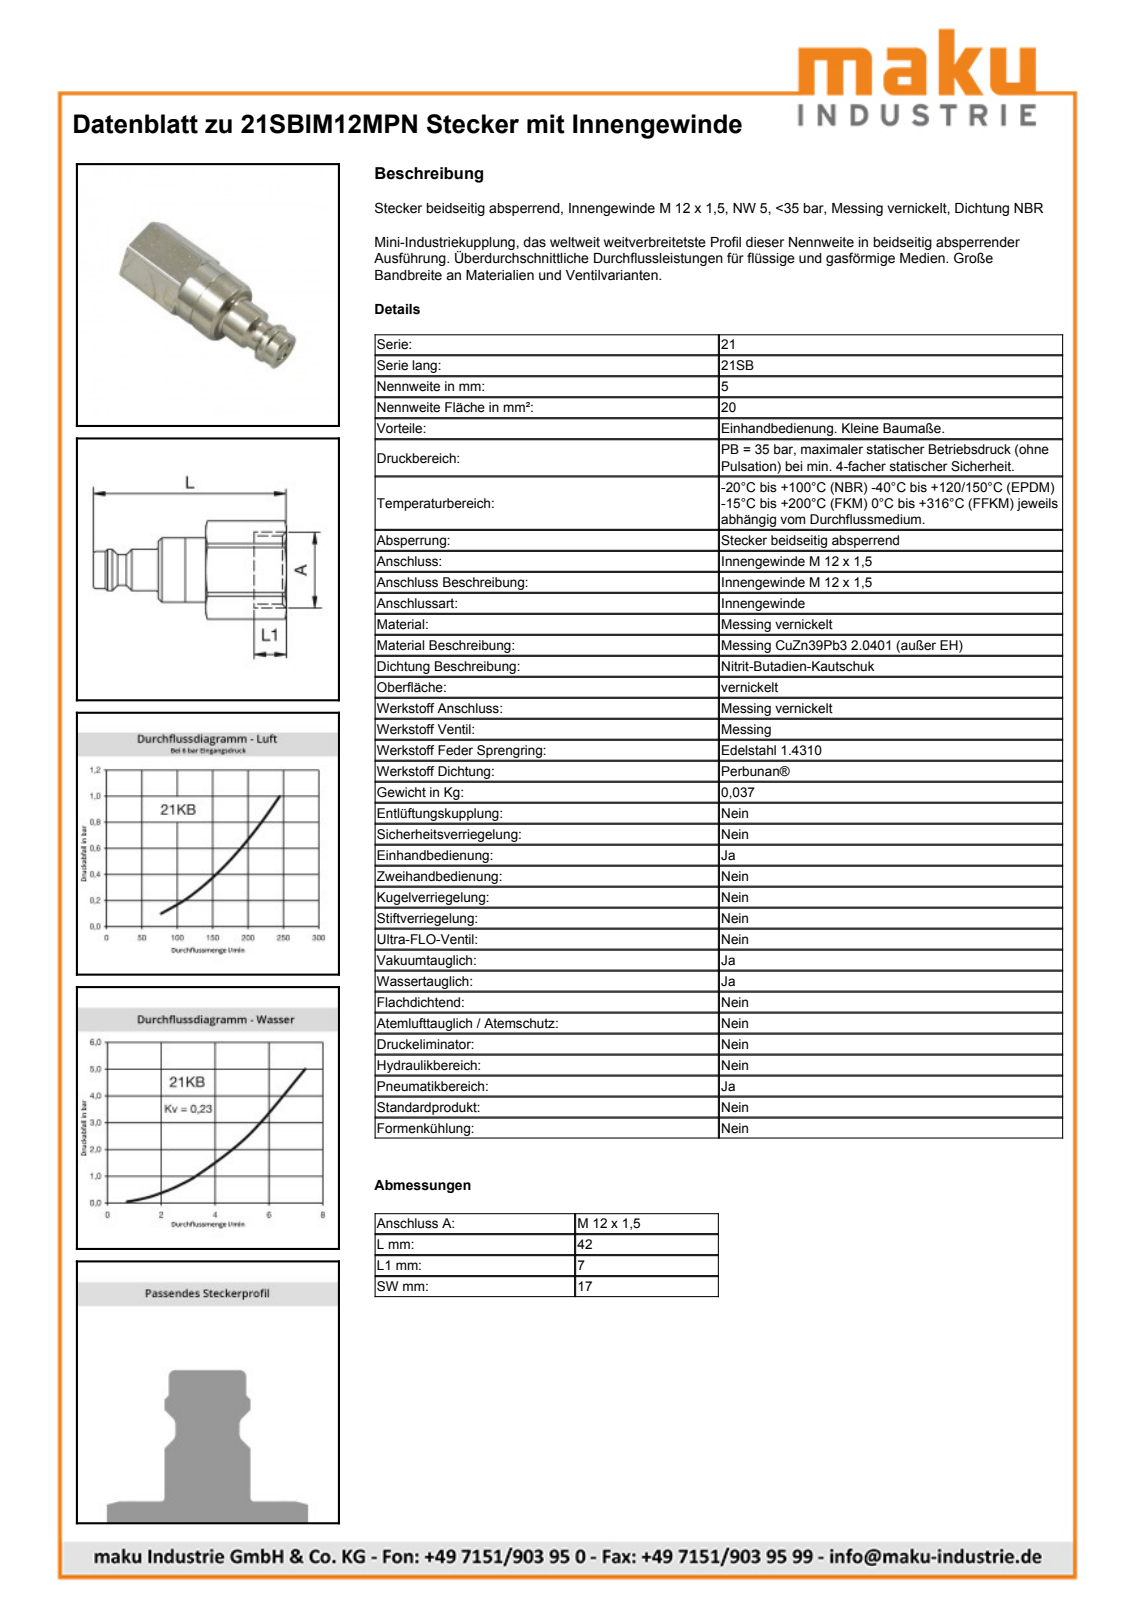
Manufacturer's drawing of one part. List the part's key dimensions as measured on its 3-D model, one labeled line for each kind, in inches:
Part name (STEP PRODUCT): D107214
STEP written by: Autodesk Inventor 2013 (AUTOMOTIVE_DESIGN)
Units: inches
Bodies: 1 solid, 56 faces (11 planar, 17 cylindrical, 28 other)
Overall size (bounding box): 1.654 × 0.737 × 0.735
Volume: 0.361 in³ · Surface area: 4.447 in²
Round holes (diameter × count): ⌀0.283 ×1, ⌀0.374 ×1, ⌀0.413 ×1, ⌀0.451 ×1
Round bosses / shafts (diameter × count): ⌀0.551 ×1, ⌀0.433 ×1, ⌀0.354 ×1, ⌀0.319 ×1, ⌀0.262 ×1, ⌀0.24 ×1
Partial cylindrical surfaces — rounded edges, fillets, slot ends (radius × count): R0.377 ×1
Main face-to-face distances: 0.669, 0.354, 0.337, 0.691, 0.407, 0.744, 1.098, 0.555, 0.963, 1.299
